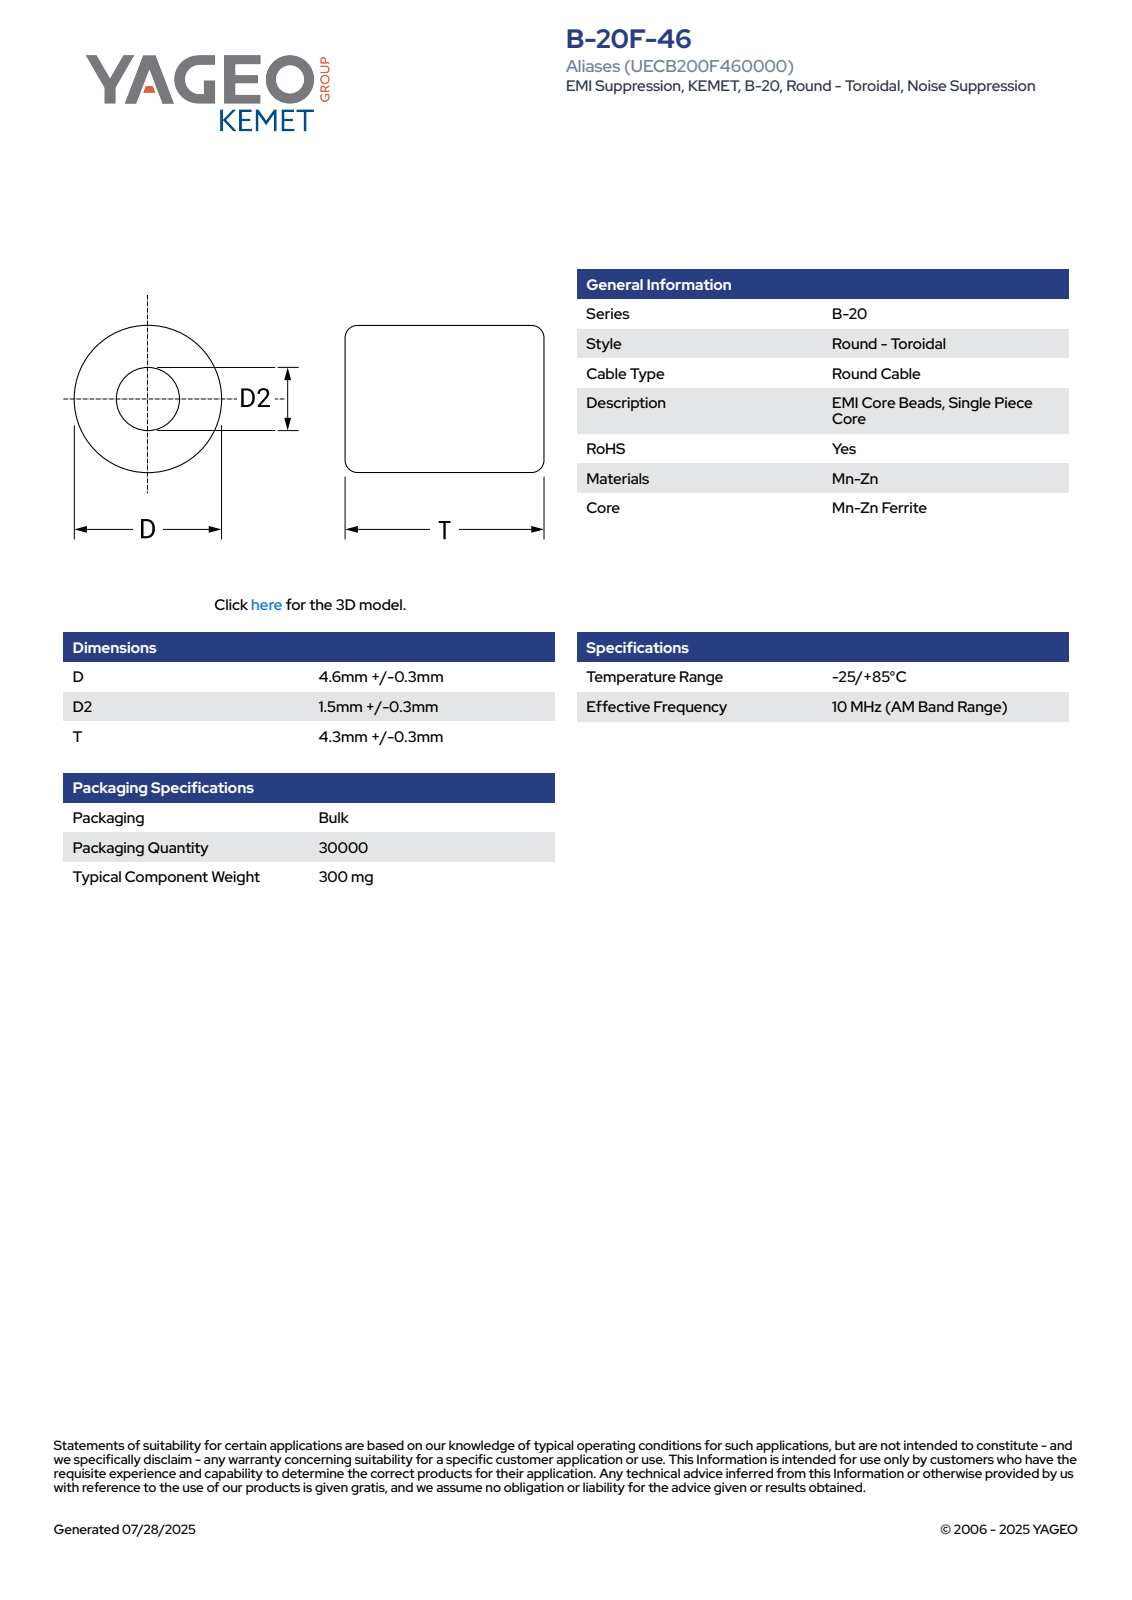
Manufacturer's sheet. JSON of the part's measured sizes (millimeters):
{"part_name": "EC_KBCH_D4.9D21.5T4.6", "step_written_by": "SolidWorks 2021 (AUTOMOTIVE_DESIGN)", "units": "millimeters", "bodies": {"solids": 1, "faces": 66, "planar": 25, "cylindrical": 7, "other": 34}, "overall_size": [4.91, 4.9, 4.6], "volume_mm3": 78, "surface_area_mm2": 125, "round_holes": [[1.5, 1]], "round_bosses_or_shafts": [[4.9, 1]], "partial_cylinders_radius": [[2.46, 1]], "face_to_face_distances": [4.6, 2.11, 2.49, 0.38, 2.18, 2.42, 0.31, 2.35, 2.25, 2.28]}
